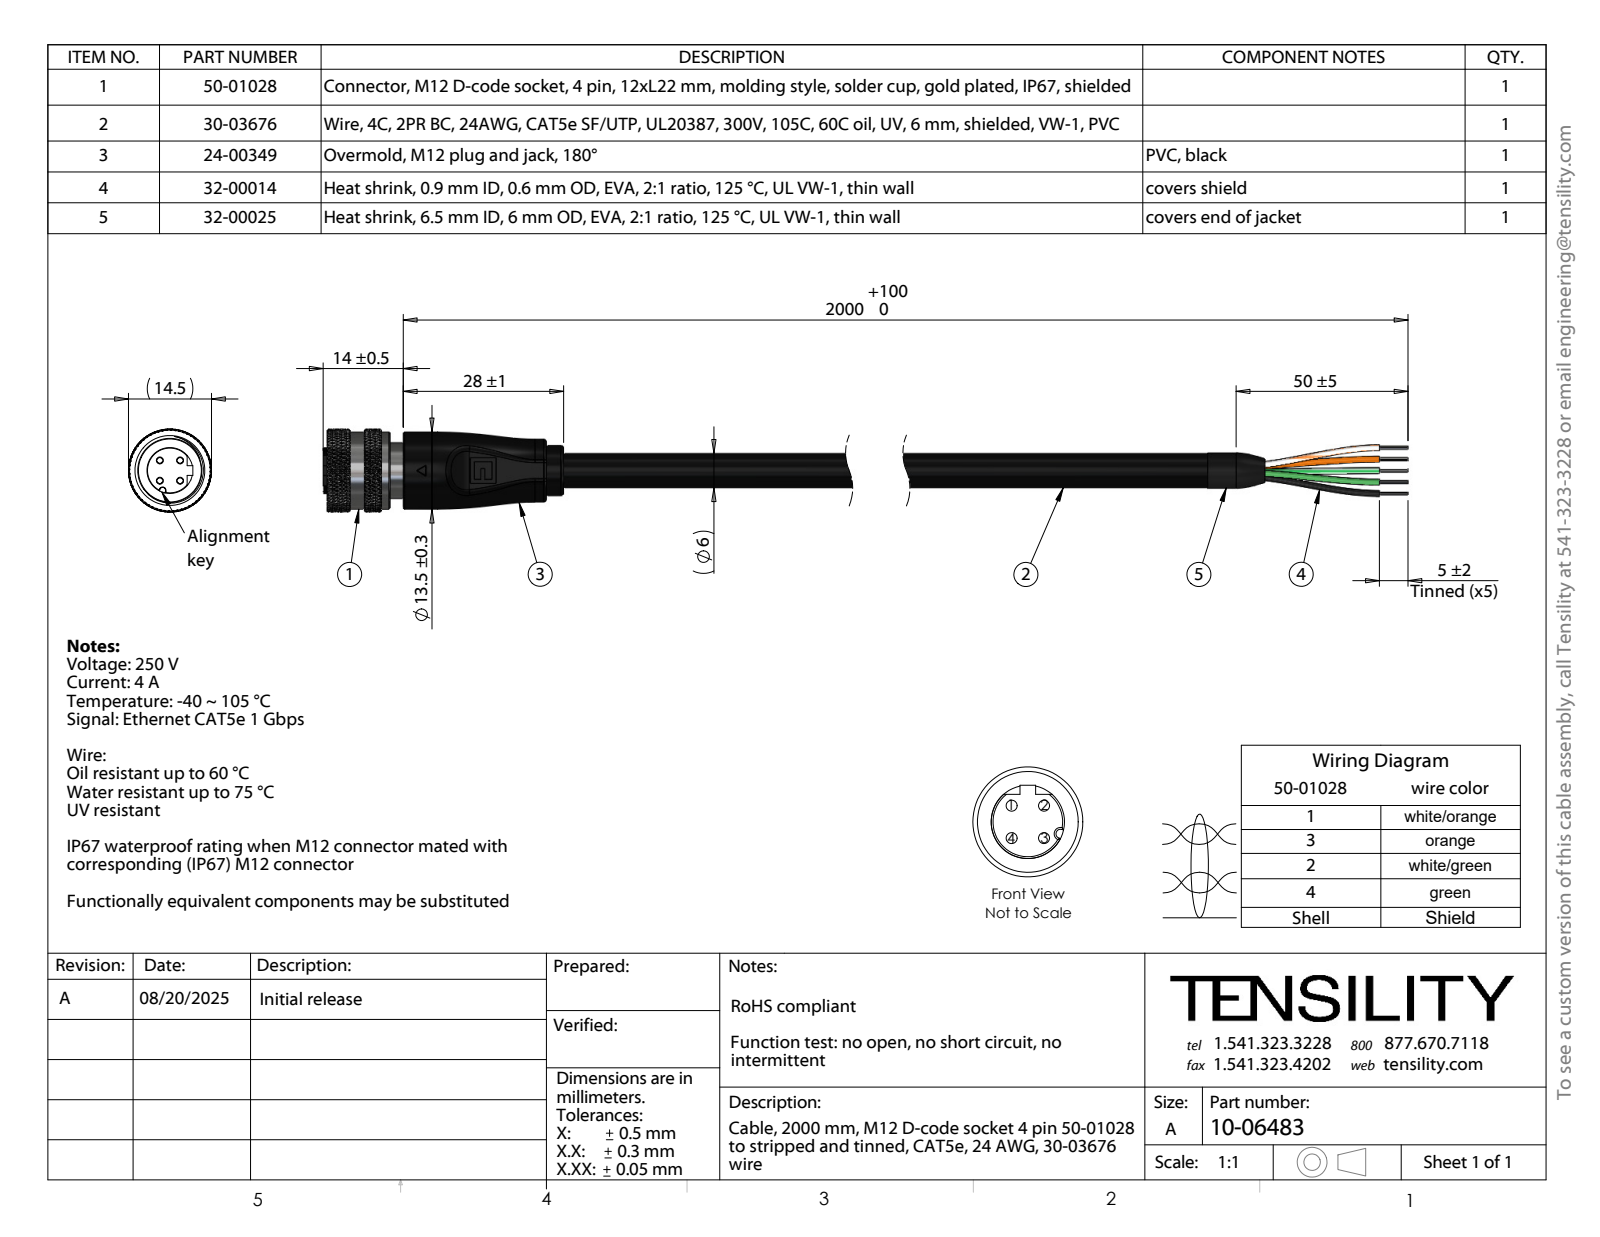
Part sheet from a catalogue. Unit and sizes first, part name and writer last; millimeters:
Units: millimetres
Overall size (bounding box): 222 × 14.5 × 14.5
Round holes (diameter × count): ⌀0.2 ×28, ⌀1.05 ×4, ⌀1.1 ×4, ⌀1.2 ×4, ⌀3.16 ×1, ⌀3.21 ×1, ⌀3.36 ×1, ⌀9 ×1, ⌀10 ×1, ⌀11.2 ×1
Round bosses / shafts (diameter × count): ⌀0.2 ×35, ⌀1.6 ×4, ⌀1.5 ×4, ⌀13.5 ×1, ⌀11 ×1, ⌀10.6 ×1, ⌀10.5 ×1, ⌀9.8 ×1
Partial cylindrical surfaces — rounded edges, fillets, slot ends (radius × count): R0.1 ×10, R0.4 ×6, R0.5 ×2, R1.5 ×2, R4 ×1, R5 ×1, R5.58 ×1, R6.75 ×1
Main face-to-face distances: 178, 28, 150, 7, 4.7, 1, 31.8, 3.5, 23.3, 173.3
Hole centre spacings: 1.91, 0.36, 2.09, 1.06, 0.89, 1.08, 1.24, 1.8
Volume: 9 616 mm³ · Surface area: 27 027 mm²
Bodies: 87 solids, 3550 faces (339 planar, 940 cylindrical, 2271 other)
Part name (STEP PRODUCT): 10-06483; 50-01028-05_默认; 50-01028-04_默认; 30-03676_s + t (+5 more)
STEP written by: SolidWorks 2025 (CONFIG_CONTROL_DESIGN)
